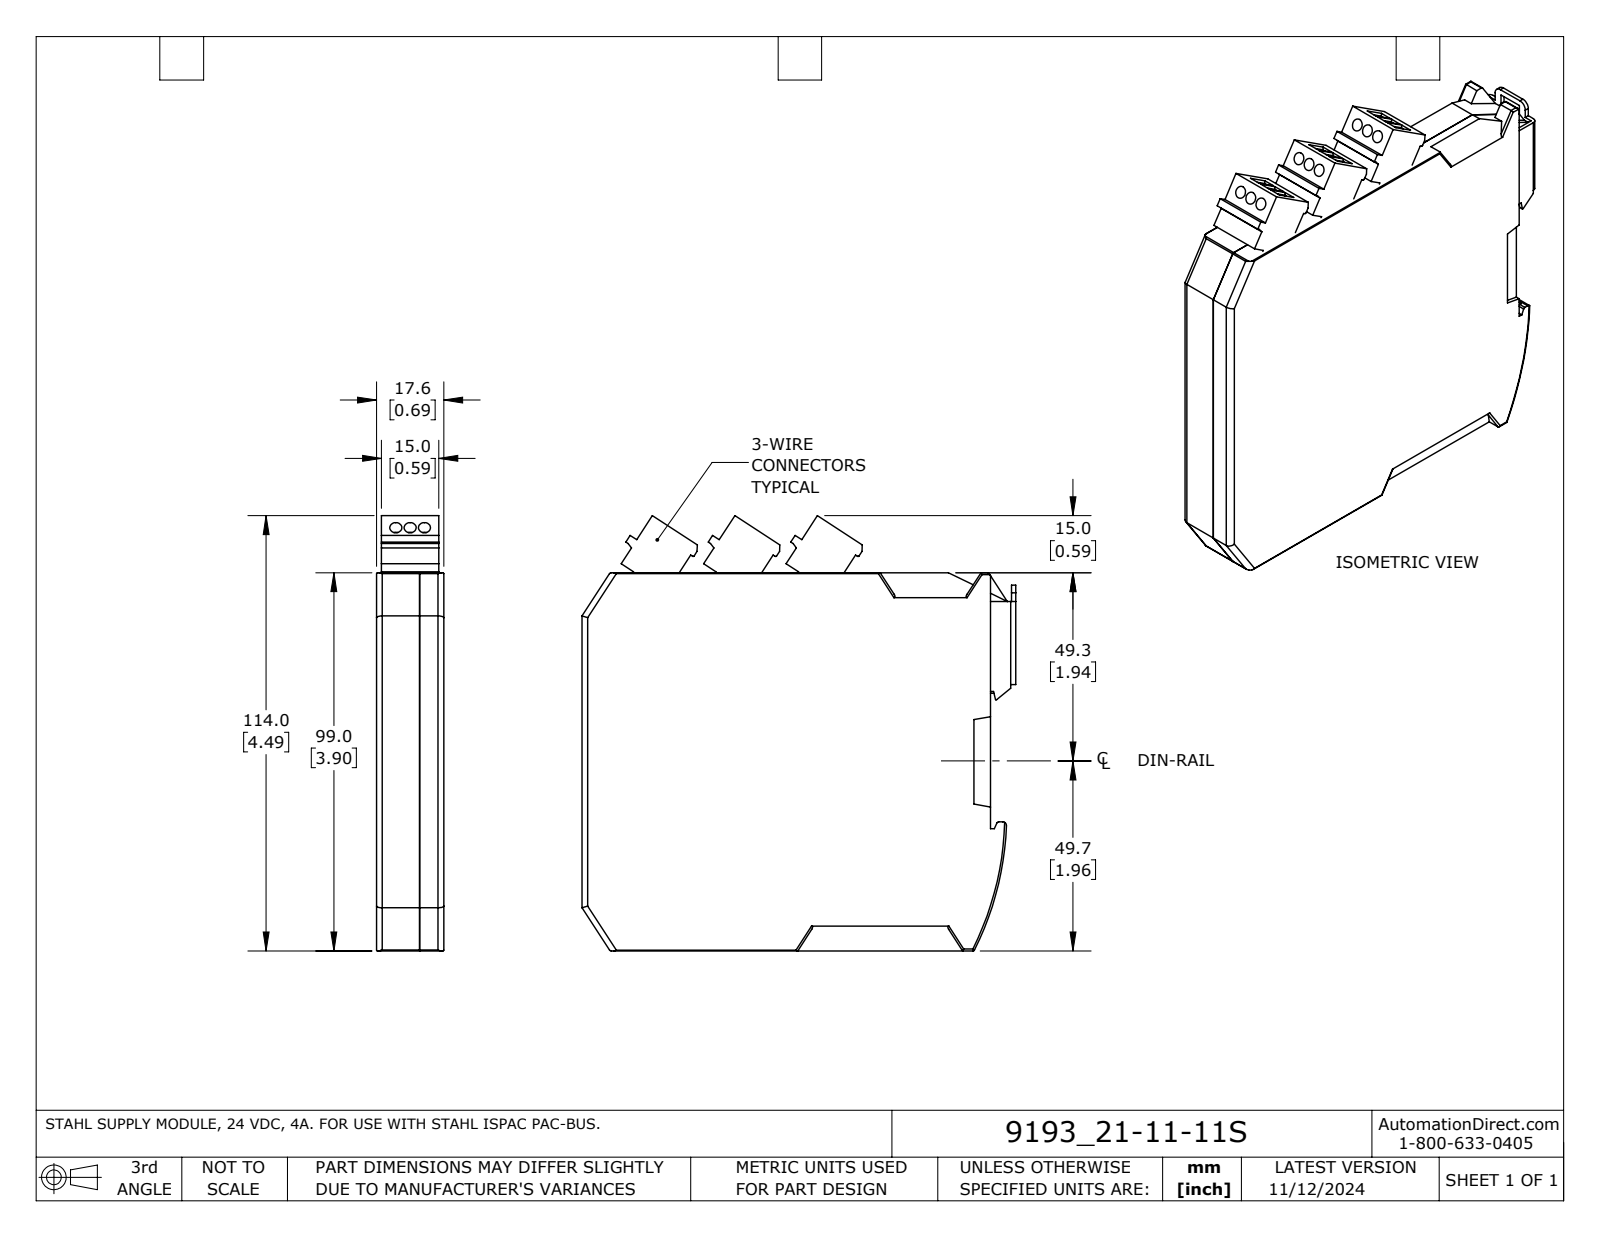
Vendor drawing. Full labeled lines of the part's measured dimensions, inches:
Part name (STEP PRODUCT): ex-9193_20-11-11-rstahl
STEP written by: SolidWorks 2023 (AUTOMOTIVE_DESIGN)
Units: inches
Bodies: 6 solids, 452 faces (349 planar, 101 cylindrical, 2 other)
Overall size (bounding box): 4.486 × 4.472 × 0.693
Volume: 12.1 in³ · Surface area: 89.33 in²
Round holes (diameter × count): ⌀0.125 ×6, ⌀0.125 ×3
Partial cylindrical surfaces — rounded edges, fillets, slot ends (radius × count): R0.02 ×17, R0.012 ×9, R0.115 ×9, R0.008 ×7, R0.059 ×6, R0.028 ×4, R0.03 ×3, R0.051 ×2
Main face-to-face distances: 0.693, 0.248, 0.445, 0.051, 0.642, 3.898, 0.591, 0.197, 0.394, 0.713
Hole centre spacings: 0.486, 0.148, 0.463, 0.938, 0.295, 0.927, 0.549, 0.55
